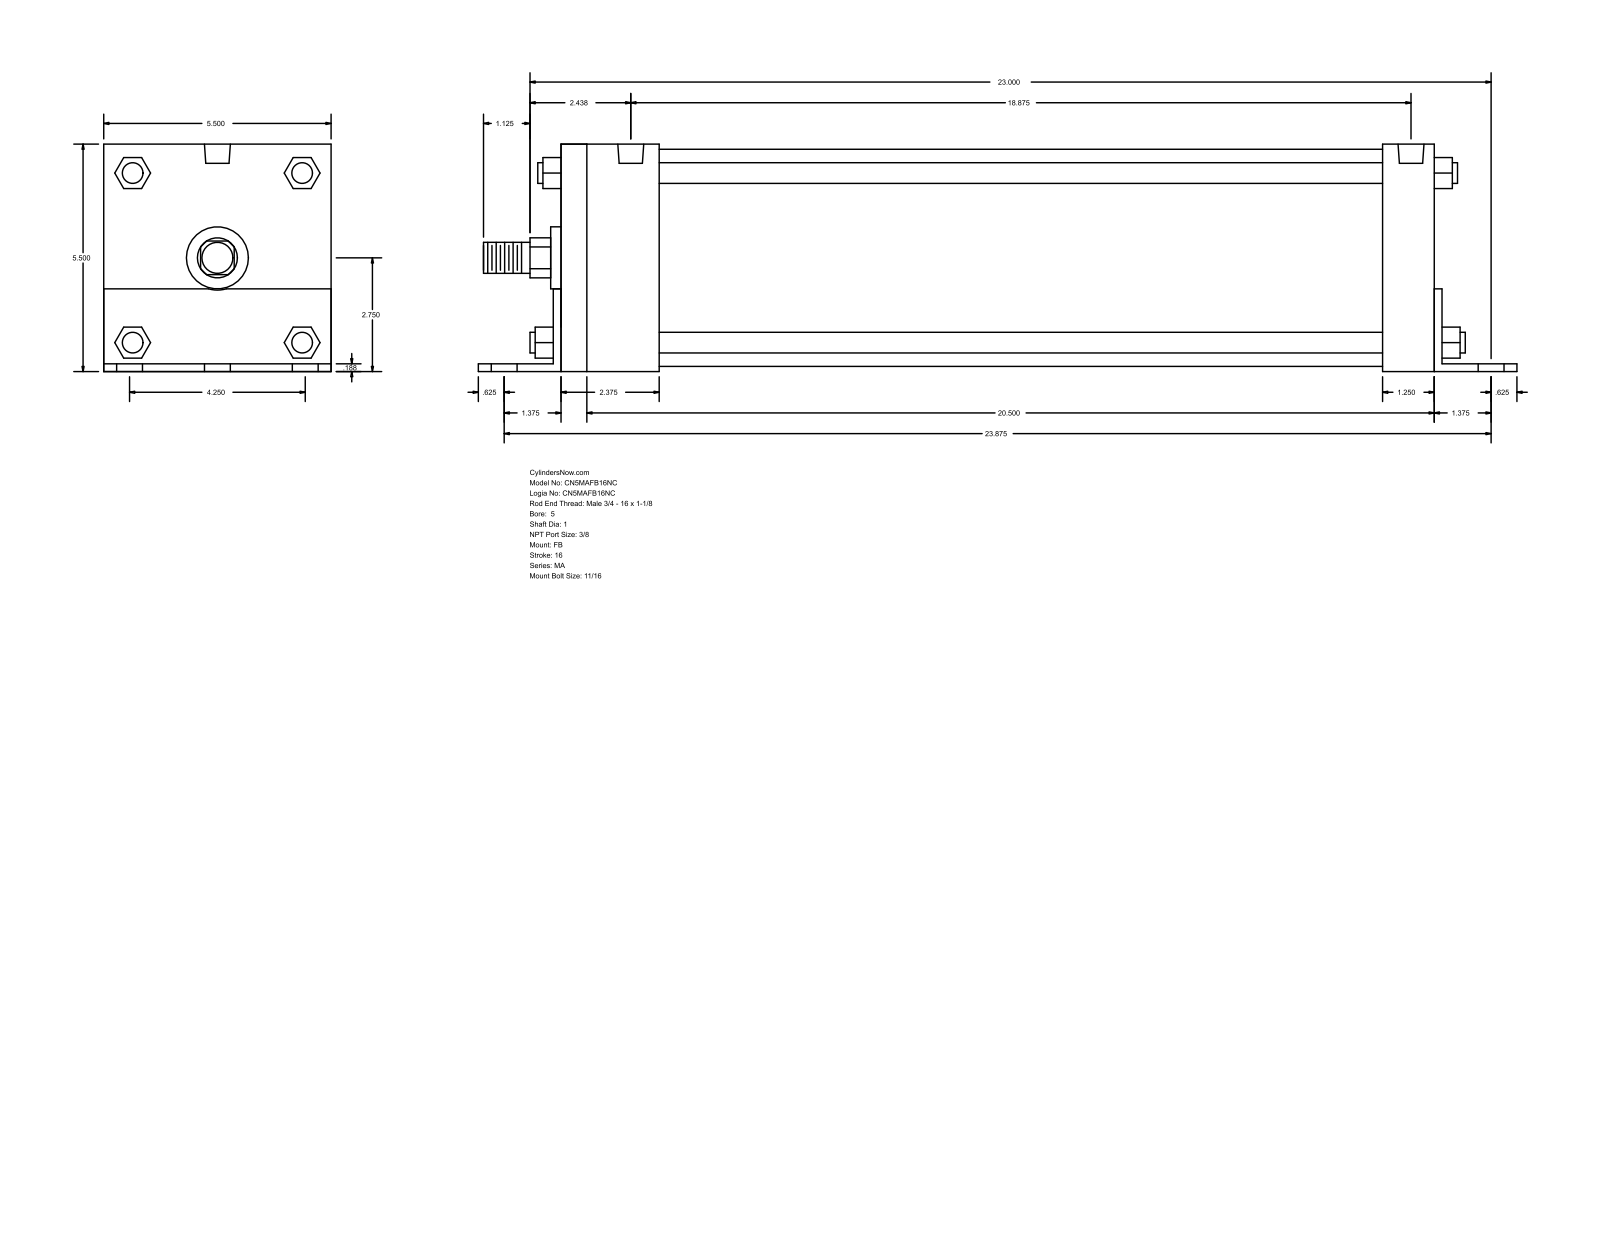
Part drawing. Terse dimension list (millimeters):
name: MA_FB__0500_1
written by: GSSL Pune (CONFIG_CONTROL_DESIGN)
unit: mm
bodies: 0 solids, 140 faces (105 planar, 35 cylindrical, 0 other)
size: 638.17 × 139.75 × 139.7
holes: 6× ⌀17.46, 4× ⌀11.11, 2× ⌀15.93
bosses: 4× ⌀12.7, 1× ⌀133.35, 1× ⌀38.1, 1× ⌀25.4, 1× ⌀19.05
rounds: 1× R12.29, 1× R19.81
face distances: 139.7, 4.76, 139.75, 4.71, 134.99, 536.57, 4.77, 36.51, 541.34, 541.33
hole spacings: 53.98, 608.83, 606.43, 4.76, 73.04, 76.33, 94.68, 98.63
